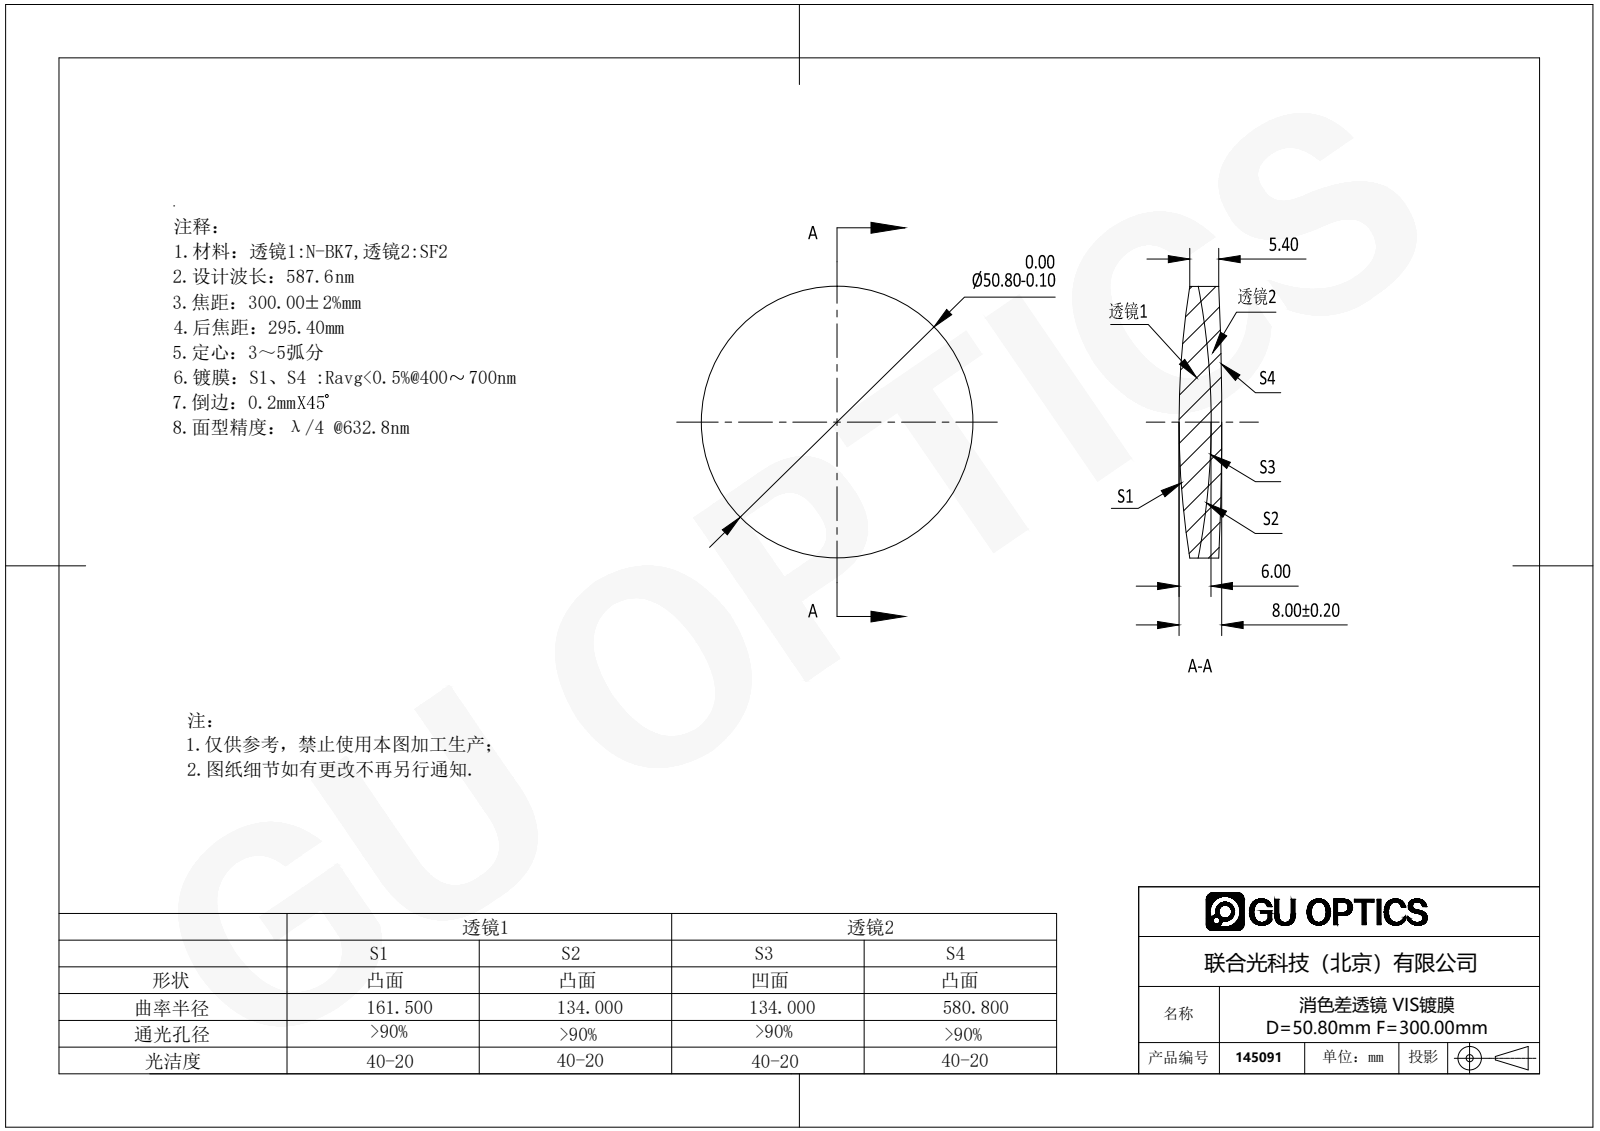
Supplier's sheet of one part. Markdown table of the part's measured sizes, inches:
| quantity | value |
| --- | --- |
| part name | 145091 |
| STEP written by | SolidWorks 2016 (AUTOMOTIVE_DESIGN) |
| units | inches |
| bodies | 2 solids, 12 faces (0 planar, 4 cylindrical, 8 other) |
| overall size | 2 × 2 × 0.315 |
| volume | 0.831 in³ |
| surface area | 13.99 in² |
| round bosses / shafts (diameter × count) | 2 × 1 |
